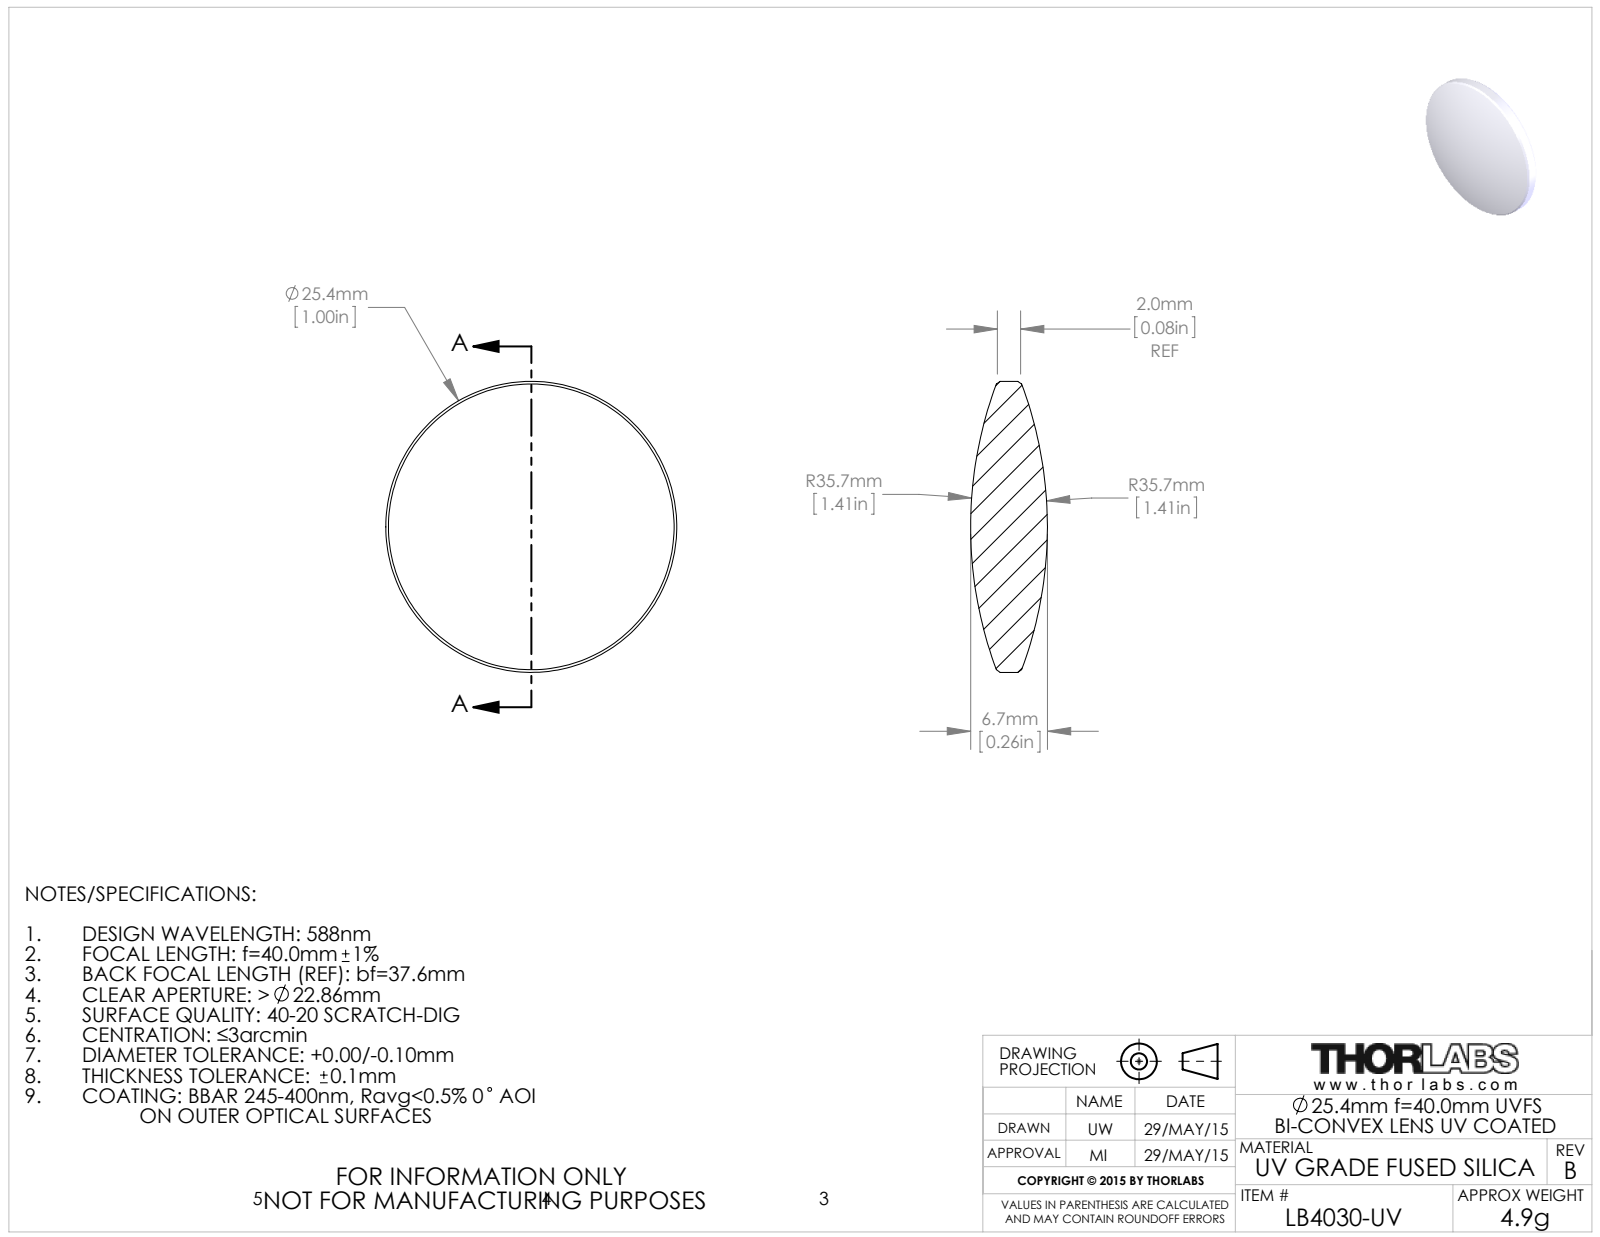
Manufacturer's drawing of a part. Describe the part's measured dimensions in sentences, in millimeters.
The part is named "4318-E0W". Its 3-D file was written by "SolidWorks 2014 (CONFIG_CONTROL_DESIGN)". It is 1 solid with 10 faces: 0 planar, 2 cylindrical and 8 other. Overall it measures 25.4 by 25.4 by 6.7 millimeters. Its volume is 2 220 cubic millimeters and its surface area 1 195 square millimeters. Round bosses or shafts: 1 of diameter 25.4.
